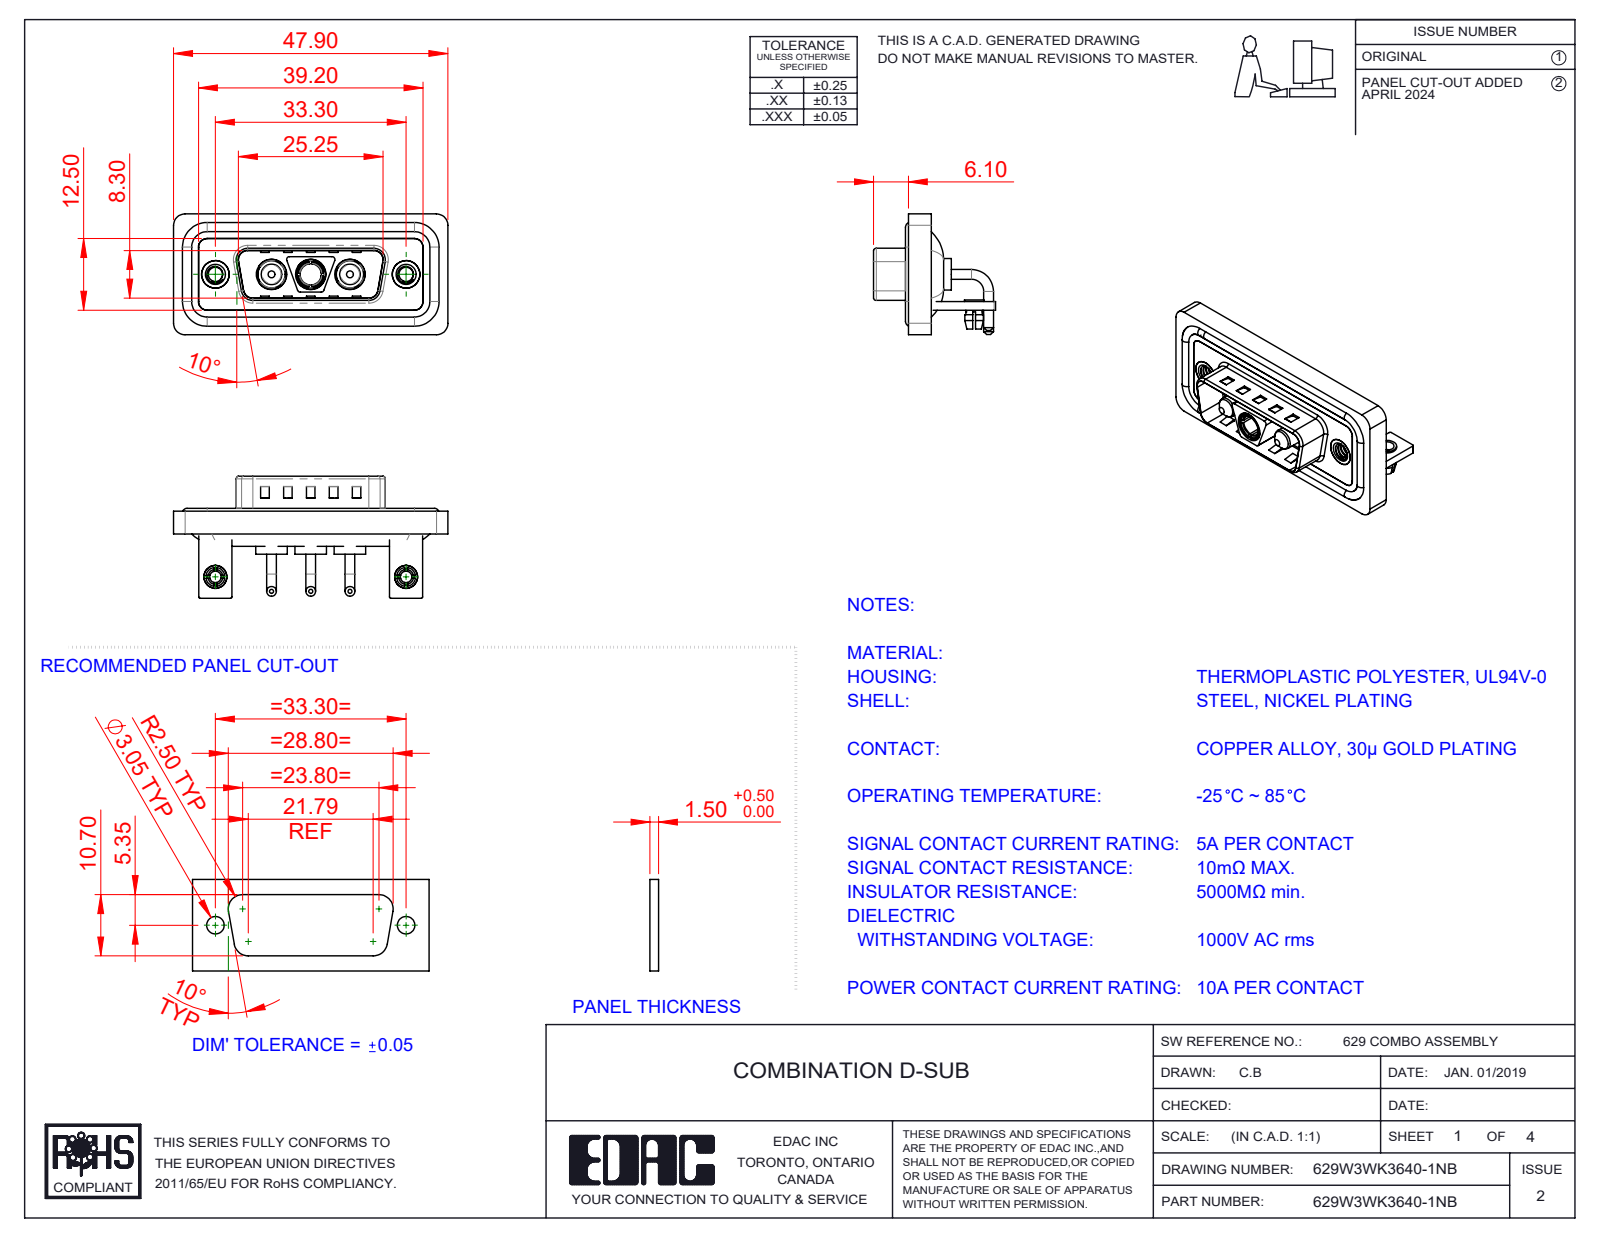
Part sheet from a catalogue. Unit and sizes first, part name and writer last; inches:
Units: inches
Overall size (bounding box): 1.886 × 0.839 × 0.831
Round holes (diameter × count): ⌀0.098 ×4, ⌀0.191 ×3, ⌀0.209 ×3, ⌀0.079 ×2, ⌀0.126 ×2, ⌀0.157 ×2, ⌀0.189 ×2, ⌀0.197 ×2, ⌀0.146 ×1
Round bosses / shafts (diameter × count): ⌀0.067 ×6, ⌀0.063 ×4, ⌀0.217 ×3, ⌀0.205 ×3, ⌀0.187 ×3, ⌀0.148 ×3, ⌀0.193 ×2, ⌀0.157 ×2
Partial cylindrical surfaces — rounded edges, fillets, slot ends (radius × count): R0.079 ×21, R0.059 ×18, R0.01 ×16, R0.02 ×13, R0.063 ×8, R0.024 ×4, R0.026 ×4, R0.035 ×4
Main face-to-face distances: 0.016, 0.059, 0.031, 0.114, 0.043, 0.083, 0.146, 0.063, 0.047, 0.177
Hole centre spacings: 0.27, 0.386, 0.656, 0.925, 1.311, 0.539
Volume: 0.367 in³ · Surface area: 15.59 in²
Bodies: 17 solids, 751 faces (299 planar, 306 cylindrical, 146 other)
Part name (STEP PRODUCT): 629Combo Board Lock; Power Pin_10A RA; 629Combo Housing_3WK3; 629W3WK3640-1NB (+6 more)
STEP written by: SolidWorks 2023 (CONFIG_CONTROL_DESIGN)
